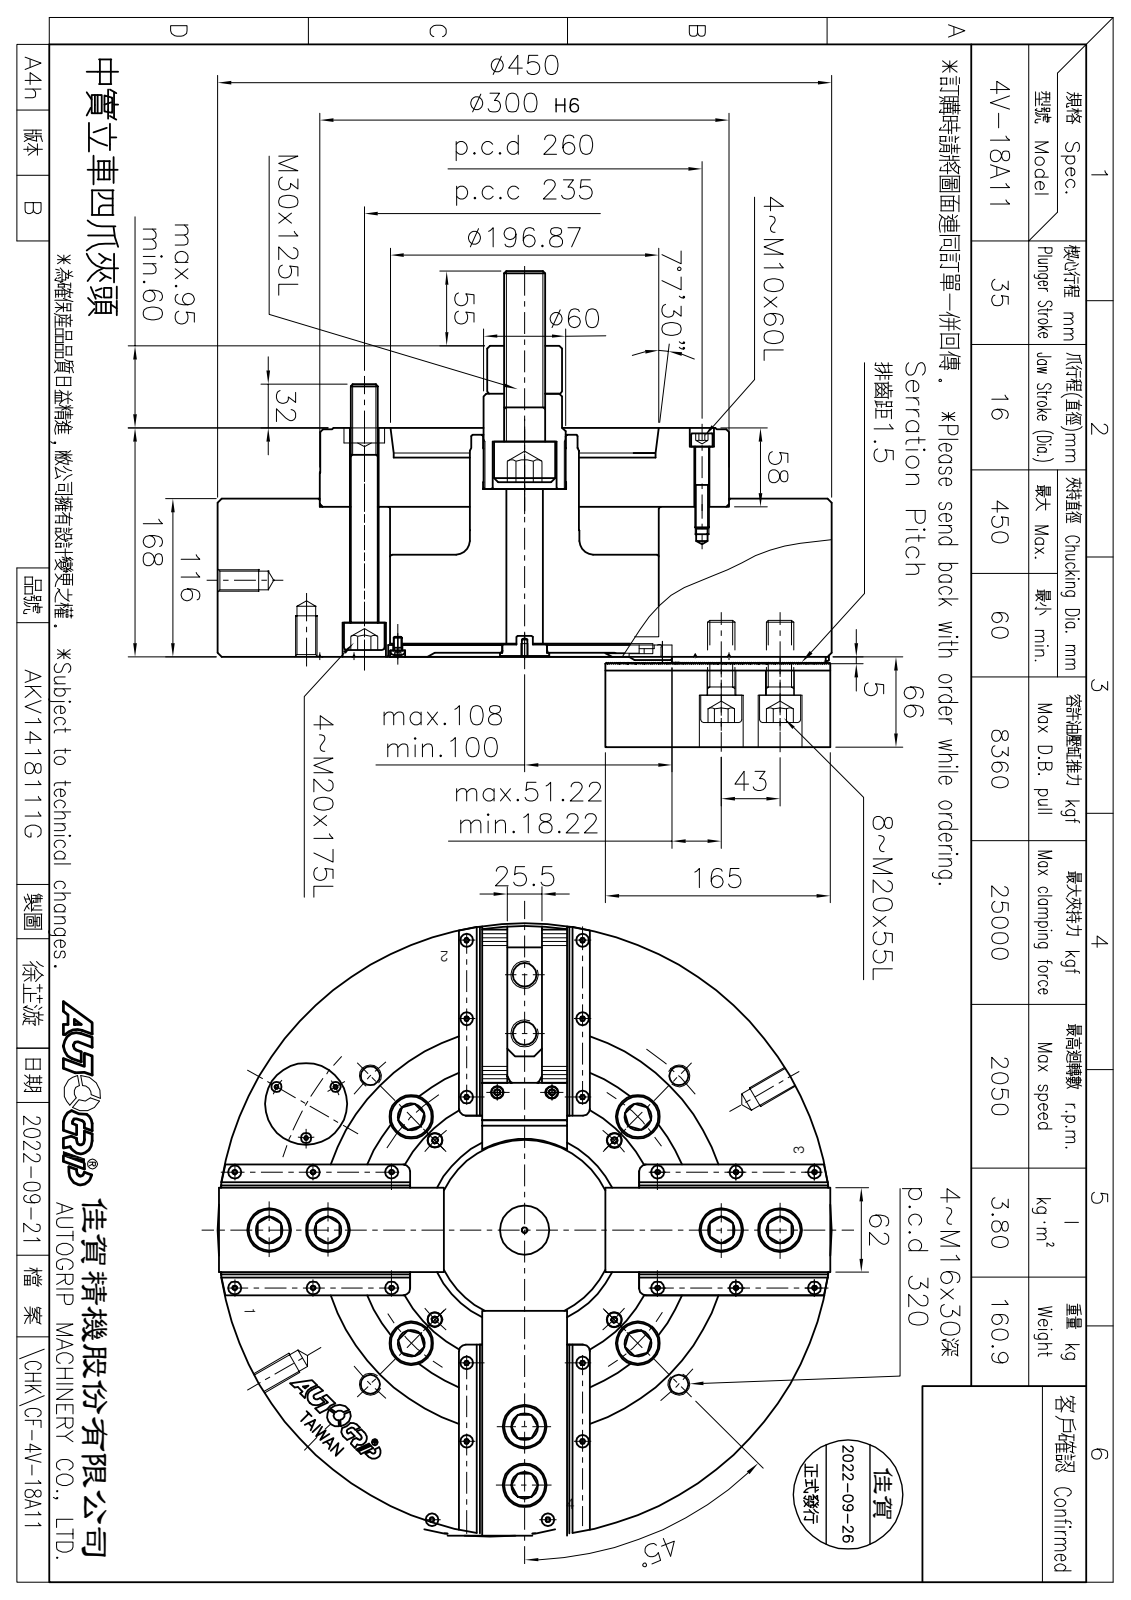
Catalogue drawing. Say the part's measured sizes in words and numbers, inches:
The part is named "CF-4V-18A11; 圓頭內六角螺栓_M20x175; CF-3P-15-06000; 半圓頭六角孔螺栓_M6x10 (+8 more)". Its 3-D file was written by "SolidWorks 2016 (CONFIG_CONTROL_DESIGN)". It is 40 solids with 7688 faces: 5035 planar, 2398 cylindrical and 255 other. Overall it measures 17.717 by 17.717 by 13.75 inches. Its volume is 1 362 cubic inches and its surface area 2 664 square inches. Round holes: 20 of diameter 0.827, 12 of diameter 1.26, 10 of diameter 0.433, 8 of diameter 0.689, 6 of diameter 0.709, 4 of diameter 0.26, 4 of diameter 0.335, 4 of diameter 0.551, 1 of diameter 0.197, 1 of diameter 1.161, 1 of diameter 1.181, 1 of diameter 1.299. Round bosses or shafts: 12 of diameter 1.181, 12 of diameter 0.787, 4 of diameter 0.63, 4 of diameter 0.413, 4 of diameter 0.394, 4 of diameter 0.236, 1 of diameter 17.717, 1 of diameter 7.047. Partial cylindrical surfaces (rounded edges, fillets, slot ends): 744 of radius 0.004, 4 of radius 0.025, 4 of radius 0.502, 4 of radius 0.709, 4 of radius 8.11, 2 of radius 0.394, 1 of radius 3.484. The main face-to-face distances are 2.283, 4.331, 2.441, 2.047, 0.236, 4.567, 0.719, 1.722, 3.996, 6.939. The hole center spacings are 5.118, 7.736, 1.362, 9.661, 5.945, 4.626, 9.004, 3.757.
